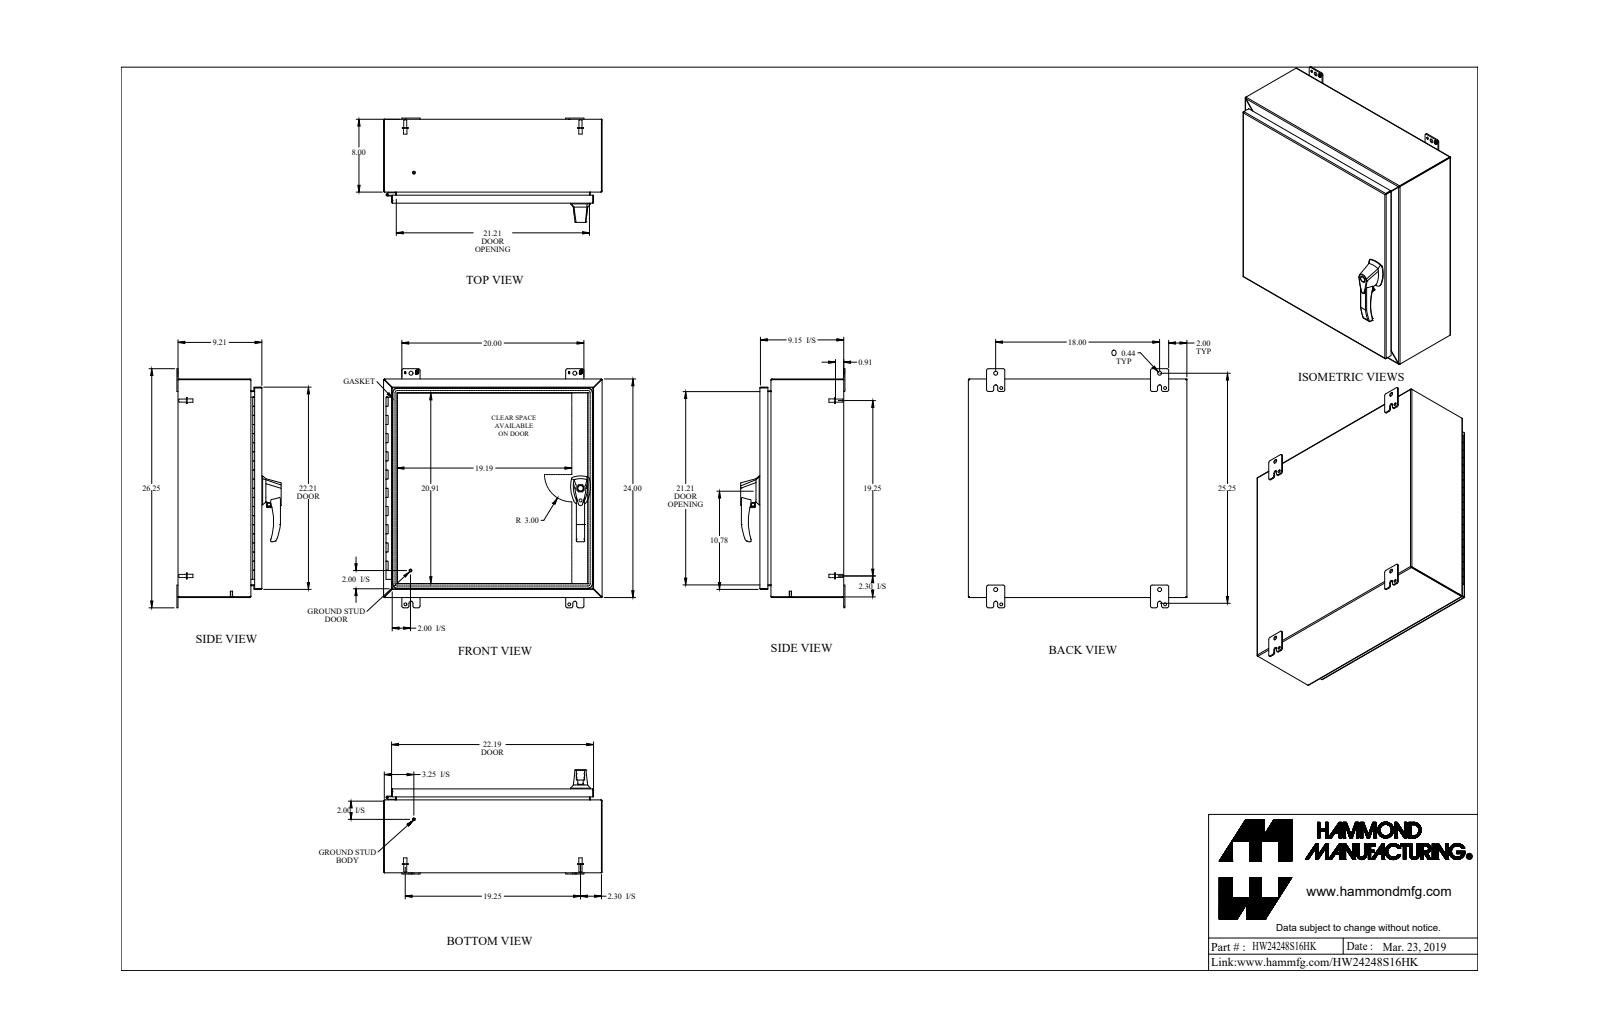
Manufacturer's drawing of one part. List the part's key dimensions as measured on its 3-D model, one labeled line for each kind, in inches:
Part name (STEP PRODUCT): HW24248S16HK
STEP written by: SolidWorks 2018 (AUTOMOTIVE_DESIGN)
Units: inches
Bodies: 42 solids, 1420 faces (688 planar, 580 cylindrical, 152 other)
Overall size (bounding box): 26.25 × 24 × 11.45
Volume: 186 in³ · Surface area: 4 770 in²
Round holes (diameter × count): ⌀0.176 ×6, ⌀0.313 ×5, ⌀0.25 ×3, ⌀0.265 ×3, ⌀0.413 ×3, ⌀0.196 ×2, ⌀0.256 ×2, ⌀0.394 ×2, ⌀0.437 ×2, ⌀0.11 ×1, ⌀0.233 ×1, ⌀0.33 ×1
Round bosses / shafts (diameter × count): ⌀0.375 ×9, ⌀0.25 ×7, ⌀0.156 ×6, ⌀0.65 ×4, ⌀0.332 ×4, ⌀1 ×3, ⌀0.51 ×3, ⌀0.63 ×2
Partial cylindrical surfaces — rounded edges, fillets, slot ends (radius × count): R0.25 ×27, R0.188 ×24, R0.036 ×20, R0.108 ×20, R0.06 ×12, R0.125 ×9, R0.045 ×8, R0.218 ×8
Main face-to-face distances: 0.072, 23.928, 0.072, 9.138, 9.066, 9.138, 9.21, 23.856, 24, 7.928
Hole centre spacings: 1.11, 8.118, 8.119, 16.237, 8.119, 18, 21.981, 1.004
